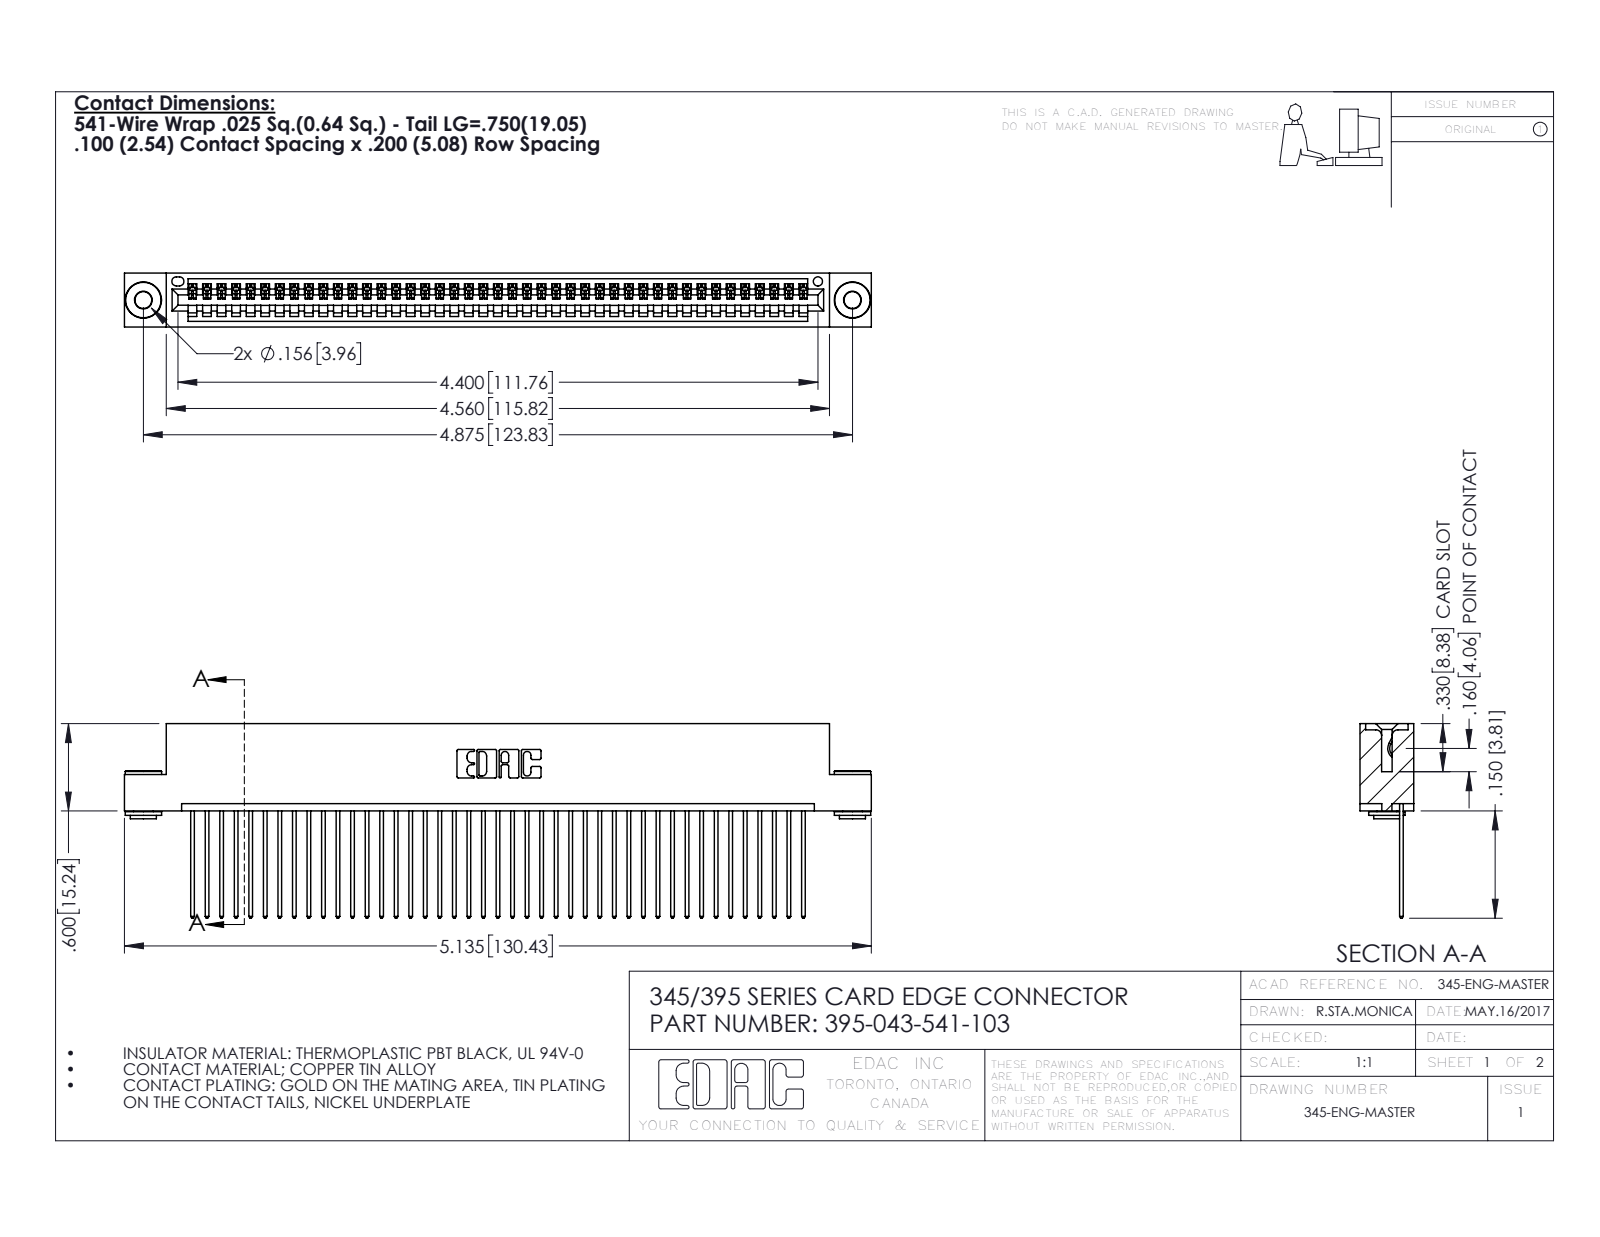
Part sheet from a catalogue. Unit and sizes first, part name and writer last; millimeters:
Units: millimetres
Overall size (bounding box): 130.4 × 34 × 9.4
Round holes (diameter × count): ⌀2.9 ×2, ⌀4 ×2, ⌀1.6 ×1
Round bosses / shafts (diameter × count): ⌀6.4 ×2, ⌀4.6 ×2, ⌀3.5 ×2
Partial cylindrical surfaces — rounded edges, fillets, slot ends (radius × count): R0.2 ×86, R0.3 ×86, R0.3 ×22, R0.2 ×6, R0.8 ×6, R0.7 ×3, R0.8 ×2, R1 ×2
Main face-to-face distances: 1.8, 7.6, 0.6, 2.5, 6.9, 9.4, 5.1, 5.7, 3.8, 1.8
Hole centre spacings: 6.9, 117.8, 123.8
Volume: 12 600 mm³ · Surface area: 17 750 mm²
Bodies: 46 solids, 2658 faces (1810 planar, 840 cylindrical, 8 other)
Part name (STEP PRODUCT): 345-292-001_345-293-141; 345 Part_Flush Mounting Lugs - 0.156 Dia-TH; 345-250-002_345-250-002-102; 395-043-541-103
STEP written by: SolidWorks 2016 (CONFIG_CONTROL_DESIGN)
